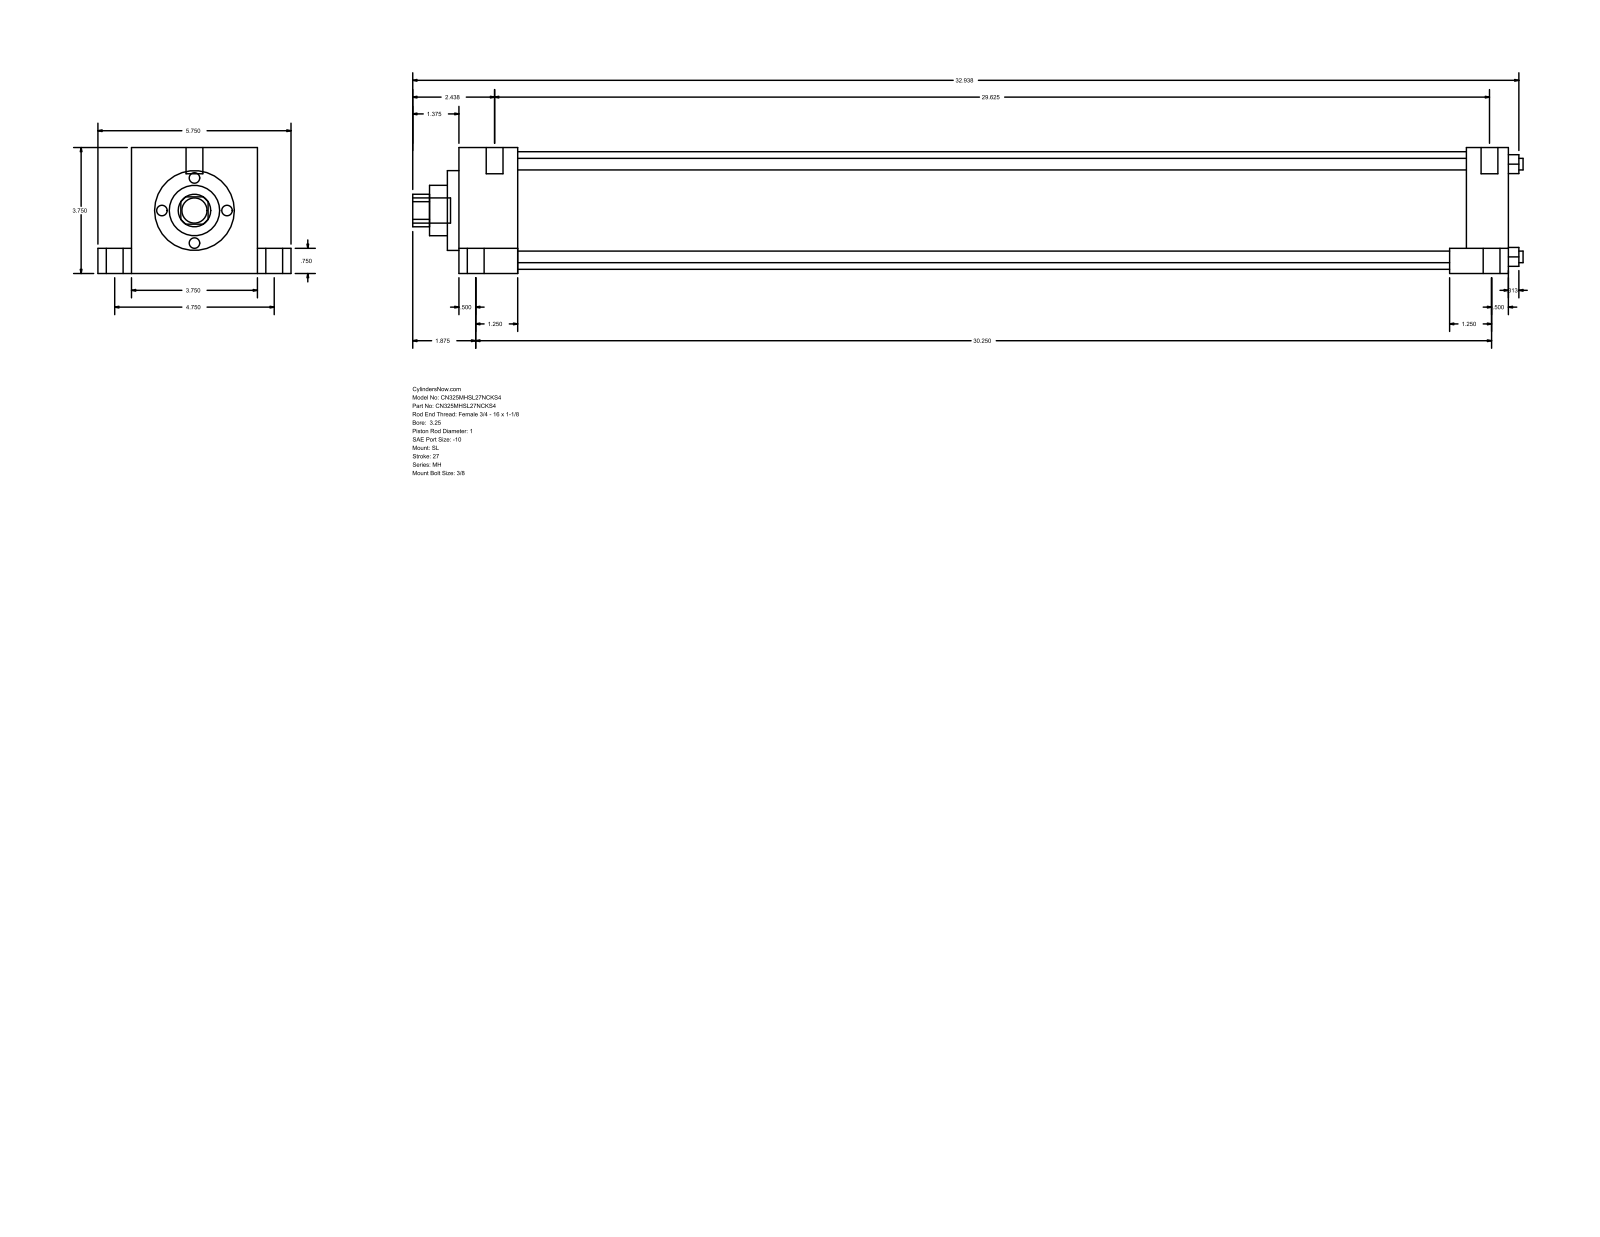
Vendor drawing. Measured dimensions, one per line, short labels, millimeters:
name: MH_SL__0325_1
written by: GSSL Pune (CONFIG_CONTROL_DESIGN)
unit: mm
bodies: 0 solids, 110 faces (77 planar, 33 cylindrical, 0 other)
size: 839.79 × 146.05 × 95.25
holes: 4× ⌀8.76, 1× ⌀25.4, 1× ⌀38.1, 1× ⌀60.33, 1× ⌀88.9
bosses: 6× ⌀12.7, 5× ⌀19.05, 4× ⌀5.56
rounds: 1× R12.29
face distances: 95.24, 793.75, 44.46, 749.29, 25.41, 120.65, 19.05, 76.19, 762, 717.54
hole spacings: 49.57, 70.1, 99.14
